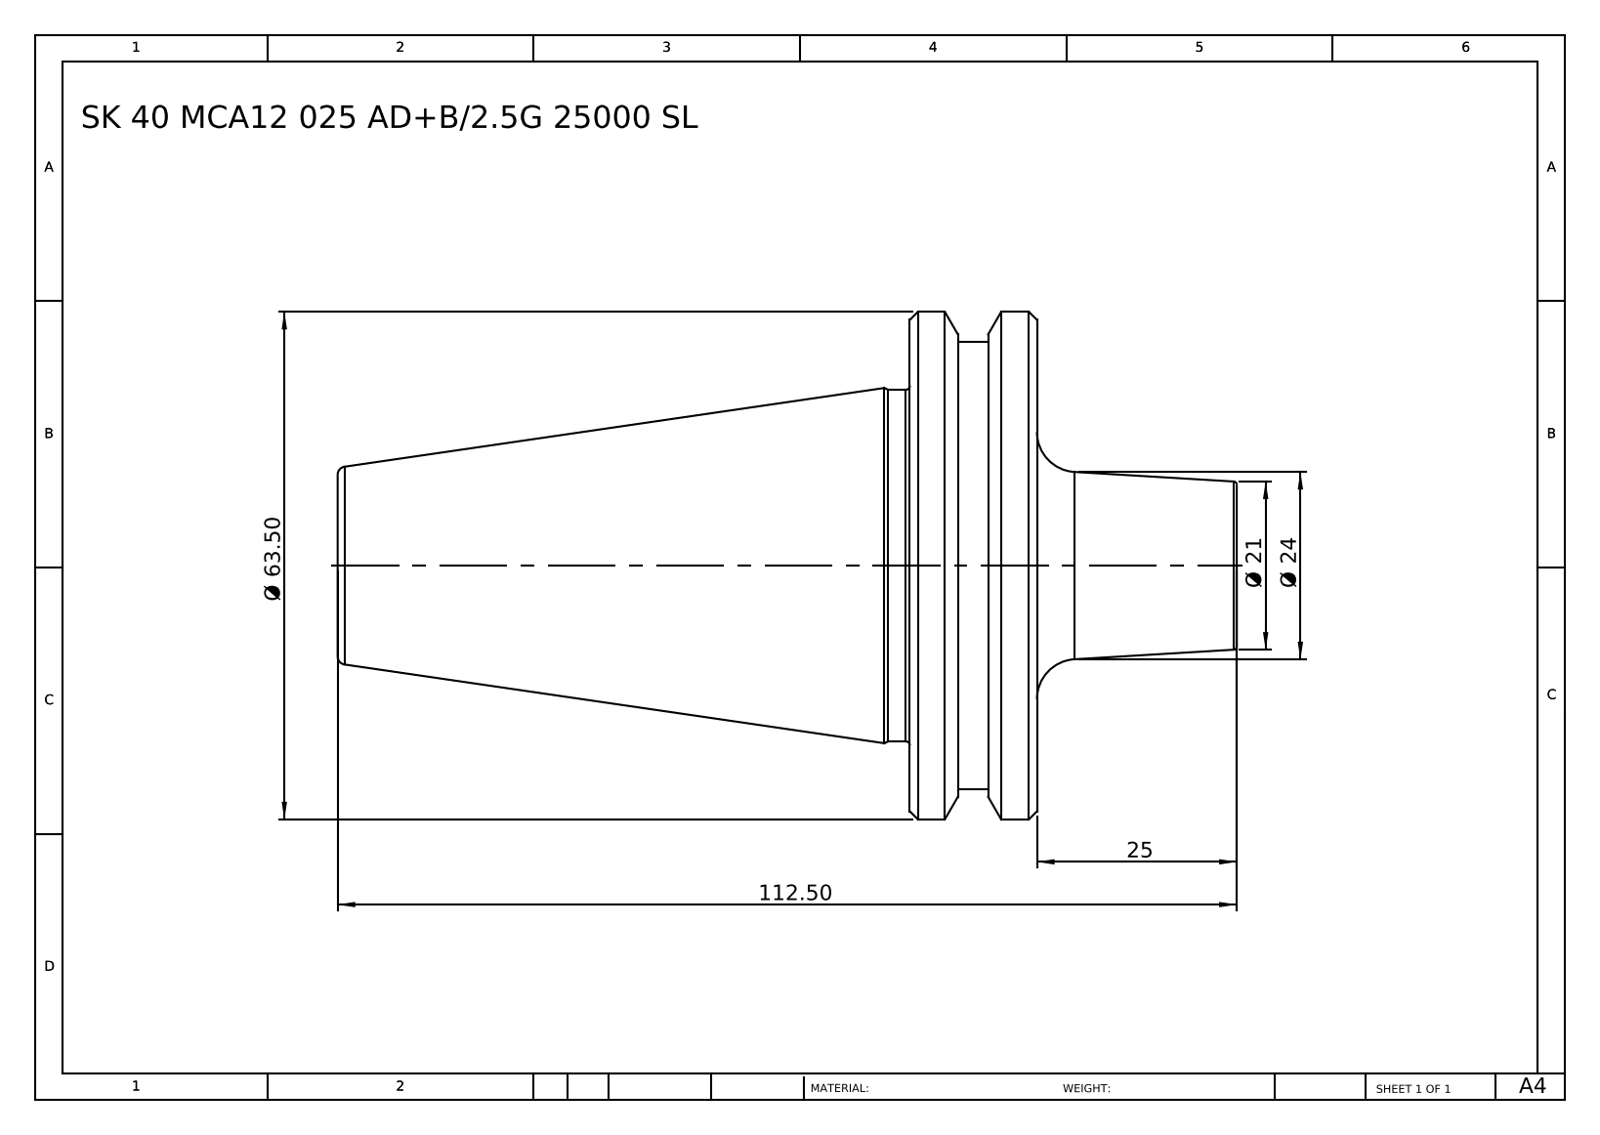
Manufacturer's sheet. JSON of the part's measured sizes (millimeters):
{"part_name": "SK 40 MCA12 025 AD+B-2.5G 25000 SL", "step_written_by": "SolidWorks 2014 (CONFIG_CONTROL_DESIGN)", "units": "millimeters", "bodies": {"solids": 1, "faces": 36, "planar": 6, "cylindrical": 8, "other": 22}, "overall_size": [112.5, 63.5, 63.5], "volume_mm3": 127439, "surface_area_mm2": 18466, "round_bosses_or_shafts": [[63.5, 1], [56, 1], [44, 1]], "face_to_face_distances": [15.9, 87.5, 71.6, 25, 40.9, 112.5, 31.1, 6.1, 9.8, 81.4]}
